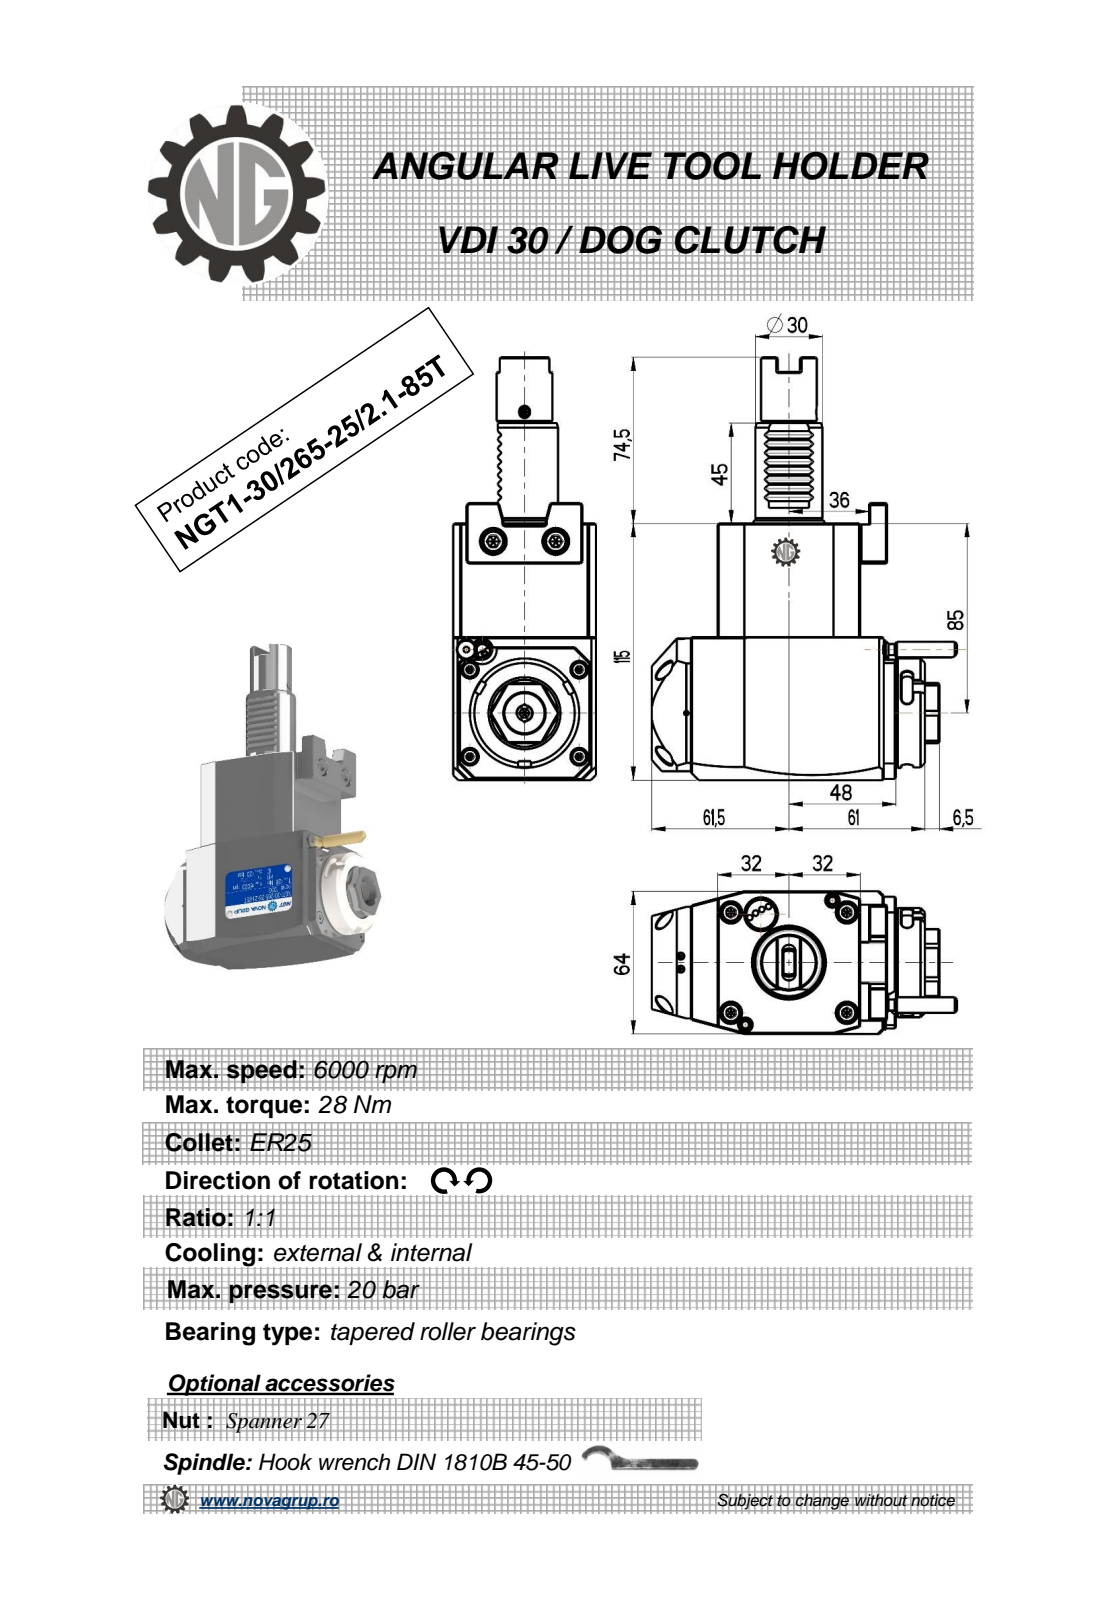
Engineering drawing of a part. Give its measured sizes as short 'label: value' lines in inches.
name: NGT1_30_265_25_1_1_85T
written by: PRO/ENGINEER BY PARAMETRIC TECHNOLOGY CORPORATION, 2010280 (CONFIG_CONTROL_DESIGN)
unit: in
bodies: 1 solid, 321 faces (200 planar, 63 cylindrical, 58 other)
size: 7.461 × 5.389 × 2.52
volume: 42 in³; area: 91.71 in²
holes: 1× ⌀0.098, 1× ⌀0.118, 1× ⌀0.165, 1× ⌀0.709
bosses: 1× ⌀1.929, 1× ⌀1.654, 1× ⌀1.181, 1× ⌀0.984, 1× ⌀0.821, 1× ⌀0.315, 1× ⌀0.276, 1× ⌀0.197
rounds: 8× R0.012, 6× R0.01, 6× R0.098, 2× R0.02, 2× R0.039, 2× R7.087, 1× R0.177, 1× R0.591
face distances: 2.52, 4.528, 3.15, 0.63, 0.157, 0.472, 3.661, 1.161, 2.008, 2.992
hole spacings: 1.348, 4.259, 5.315
